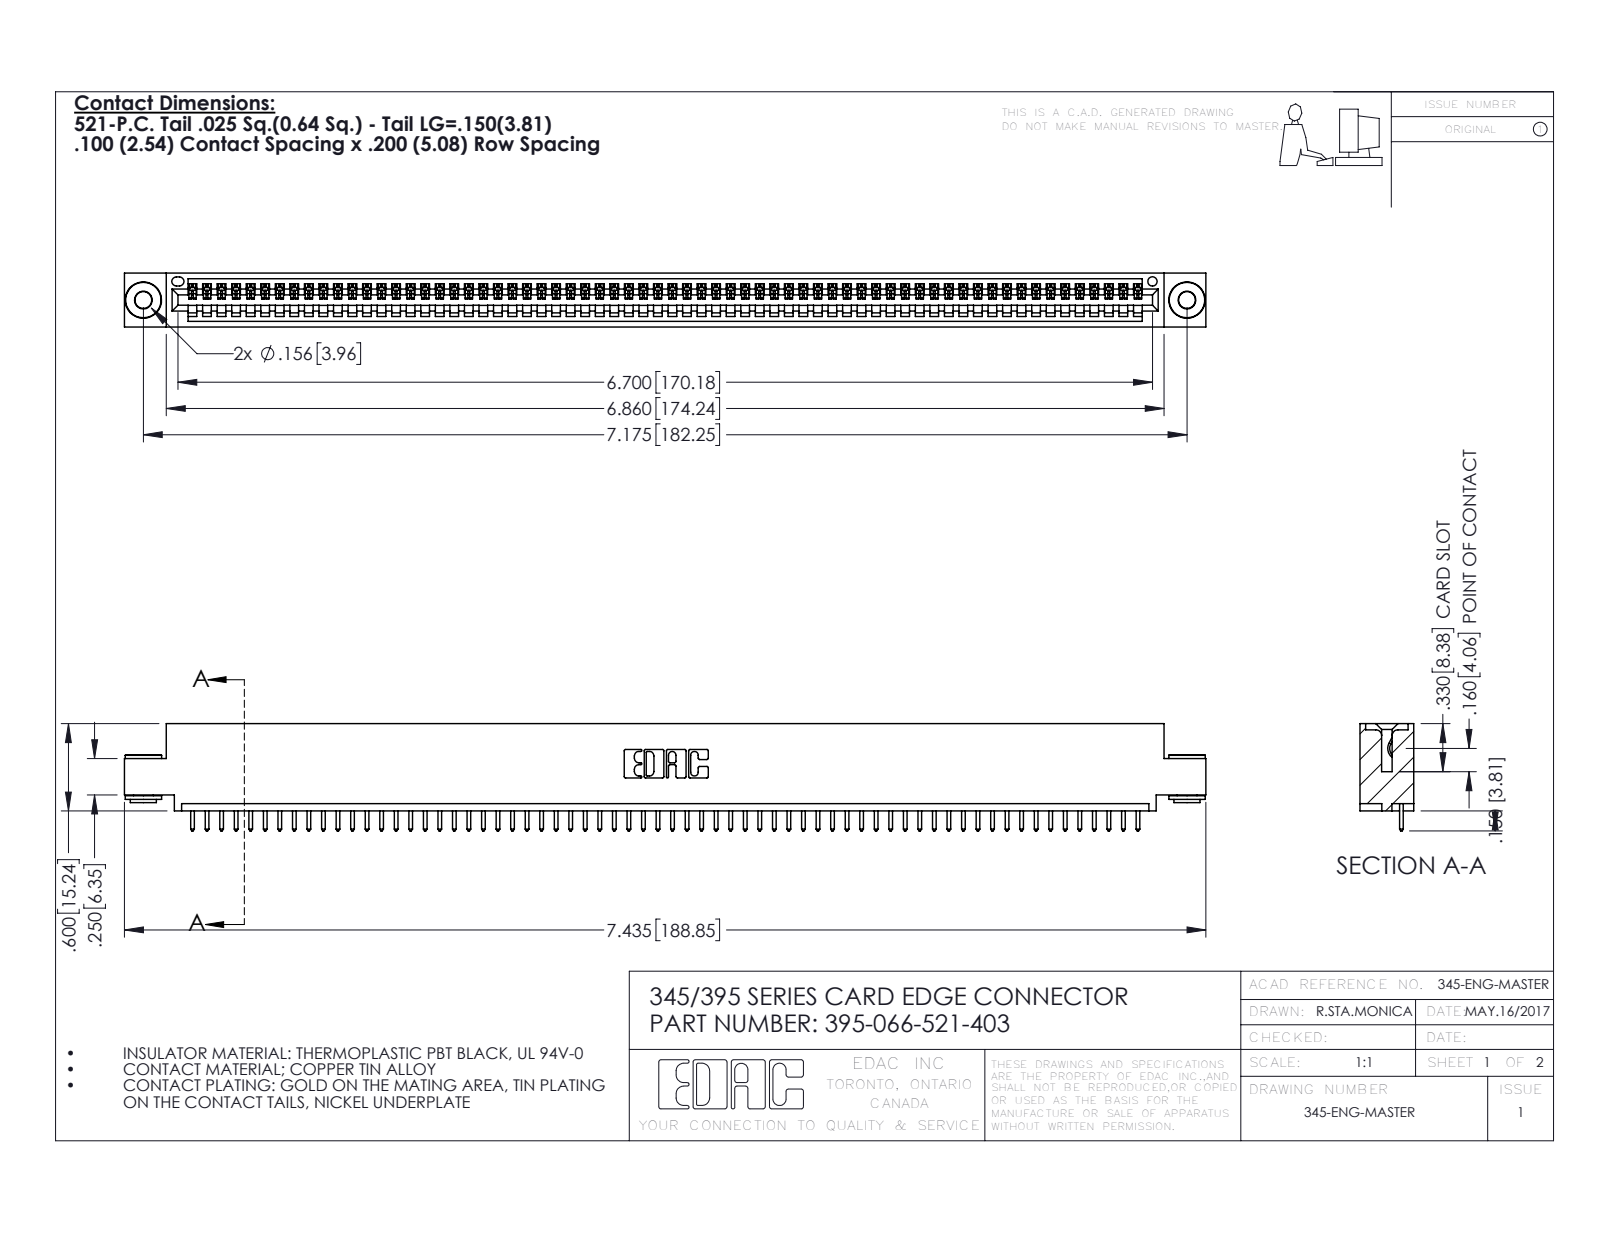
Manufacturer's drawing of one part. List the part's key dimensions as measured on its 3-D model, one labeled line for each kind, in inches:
Part name (STEP PRODUCT): 395-066-521-403; 345-250-002_345-250-002-102; 345-292-001_345-293-121; 345 Part_0.110 Offset - 0.156 Dia-TH
STEP written by: SolidWorks 2016 (CONFIG_CONTROL_DESIGN)
Units: inches
Bodies: 69 solids, 3996 faces (2734 planar, 1254 cylindrical, 8 other)
Overall size (bounding box): 7.435 × 0.737 × 0.37
Volume: 1.092 in³ · Surface area: 36.68 in²
Round holes (diameter × count): ⌀0.116 ×2, ⌀0.156 ×2, ⌀0.064 ×1
Round bosses / shafts (diameter × count): ⌀0.25 ×2, ⌀0.18 ×2, ⌀0.136 ×2
Partial cylindrical surfaces — rounded edges, fillets, slot ends (radius × count): R0.006 ×132, R0.01 ×132, R0.01 ×22, R0.007 ×6, R0.031 ×6, R0.026 ×3, R0.031 ×2, R0.04 ×2
Main face-to-face distances: 0.072, 0.298, 0.37, 0.2, 0.025, 0.098, 0.272, 0.225, 0.149, 0.072
Hole centre spacings: 0.27, 6.939, 7.175
